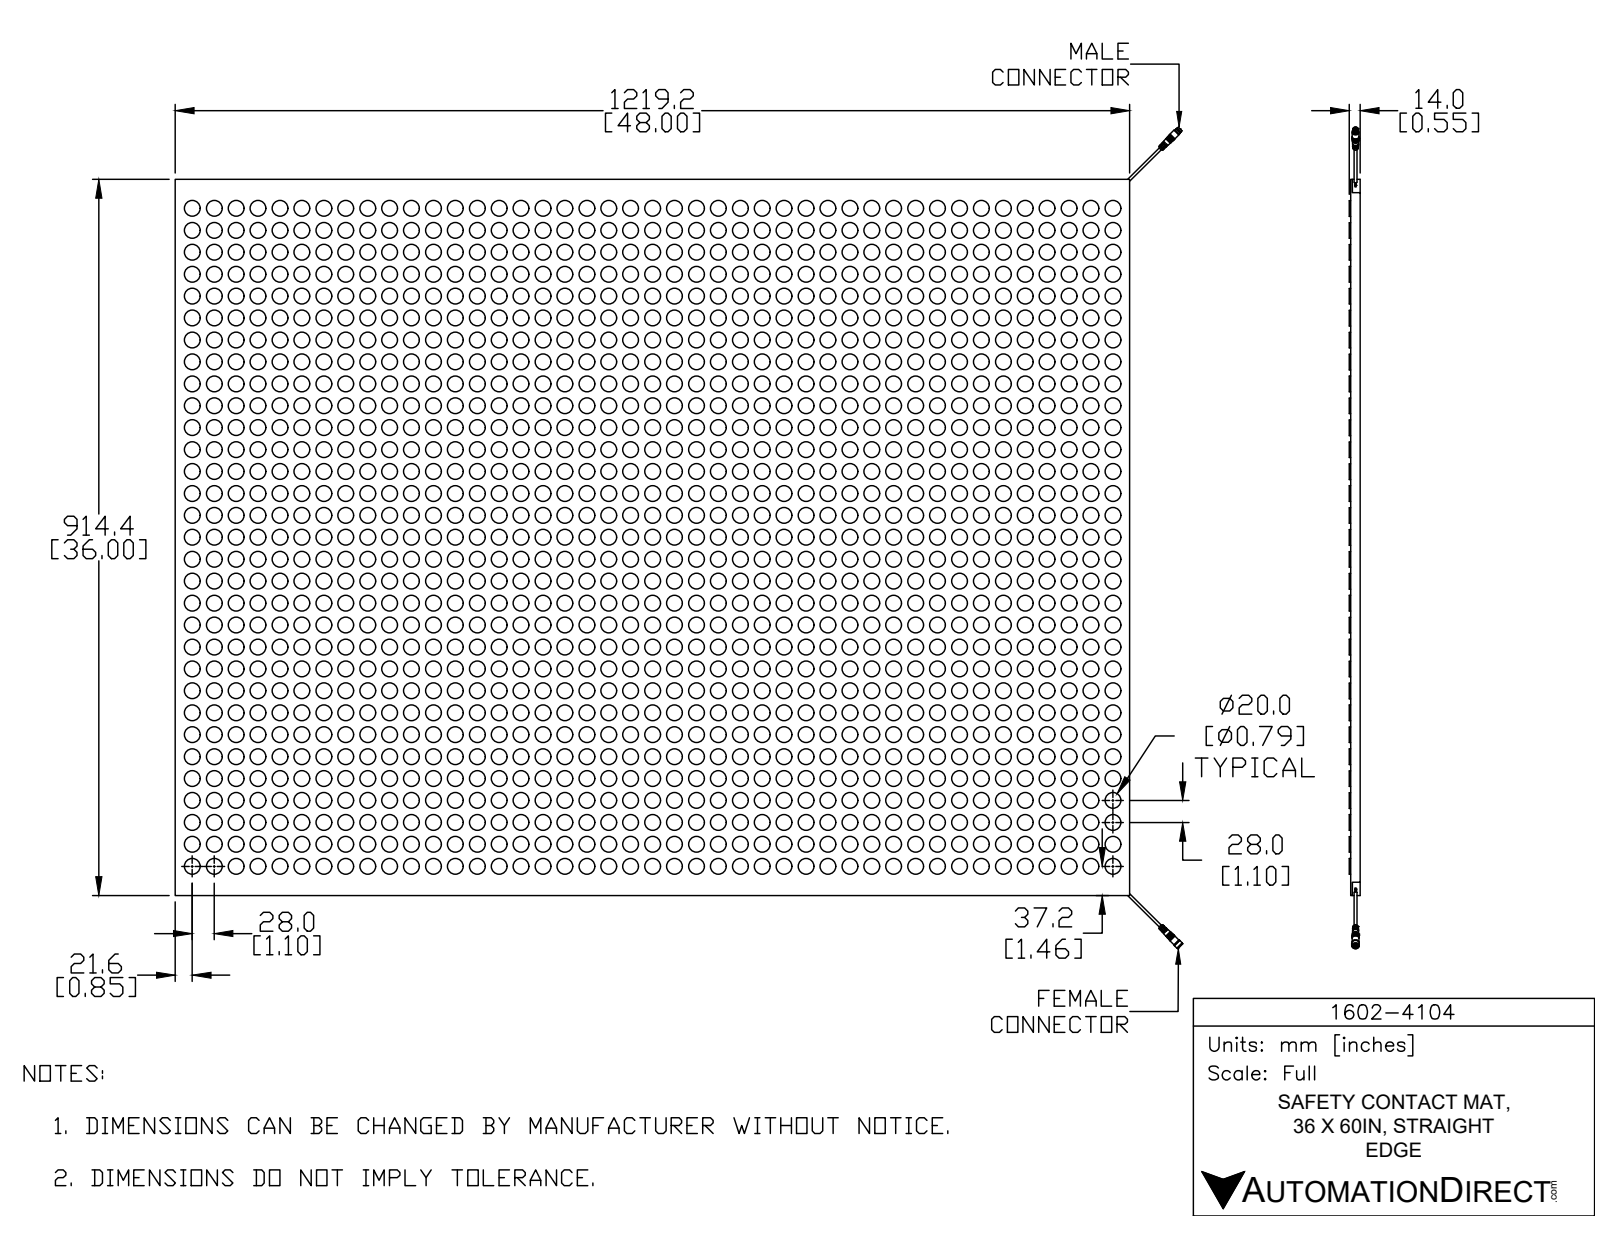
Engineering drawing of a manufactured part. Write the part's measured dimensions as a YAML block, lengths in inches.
part_name: "1602-4104_a"
step_written_by: "SolidWorks 2018 (AUTOMOTIVE_DESIGN)"
units: inches
bodies: {solids: 6, faces: 2929, planar: 1455, cylindrical: 1392, other: 82}
overall_size: [50.67, 41.295, 0.551]
volume: 867.6
surface_area: 3803
round_holes:
  - {diameter: 0.063, count: 3}
  - {diameter: 0.134, count: 2}
  - {diameter: 0.228, count: 1}
  - {diameter: 0.232, count: 1}
  - {diameter: 0.272, count: 1}
  - {diameter: 0.283, count: 1}
round_bosses_or_shafts:
  - {diameter: 0.787, count: 1333}
  - {diameter: 0.047, count: 24}
  - {diameter: 0.031, count: 8}
  - {diameter: 0.039, count: 3}
  - {diameter: 0.346, count: 2}
  - {diameter: 0.138, count: 2}
  - {diameter: 0.378, count: 1}
  - {diameter: 0.354, count: 1}
face_to_face_distances: [0.472, 0.079, 0.551, 36, 48, 0.087, 0.394, 0.157, 0.173, 0.047]
hole_center_spacings: [0.069, 0.098, 0.138]
